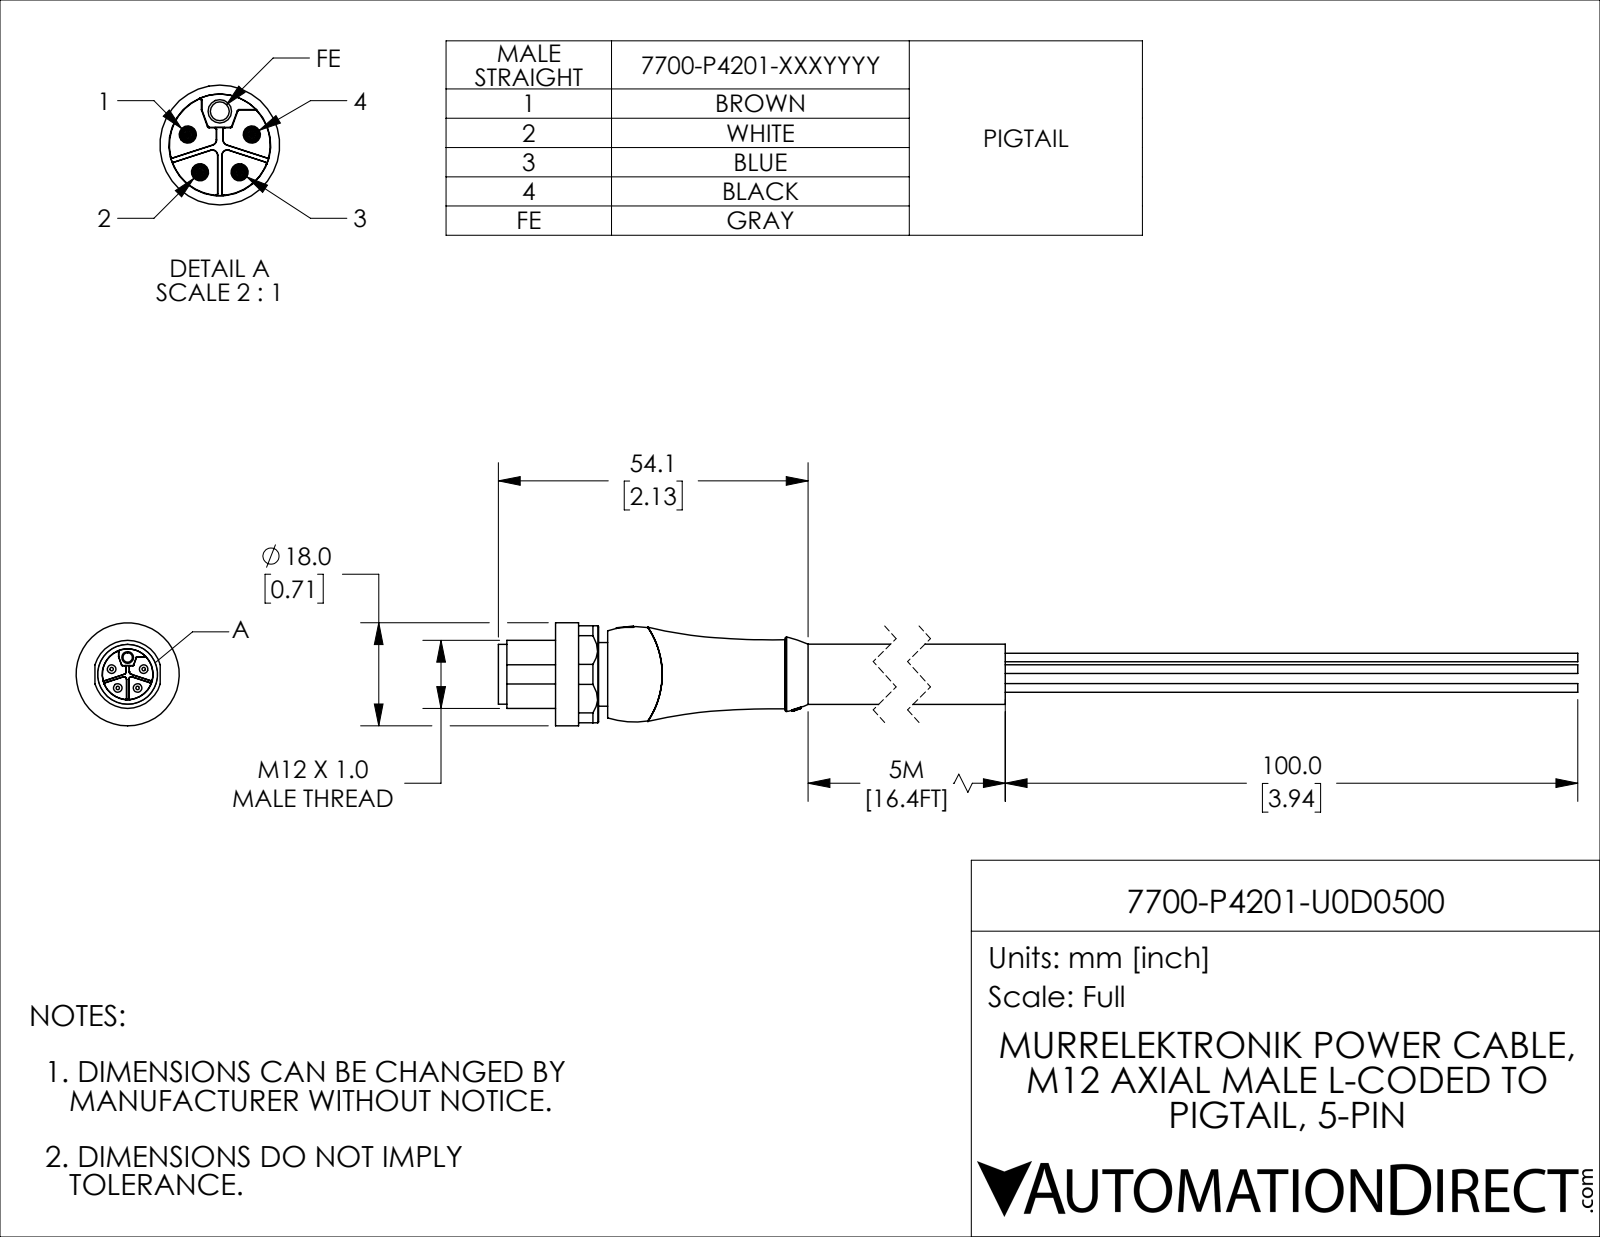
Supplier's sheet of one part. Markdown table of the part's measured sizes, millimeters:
| quantity | value |
| --- | --- |
| part name | 7700-P4201-U0D0500 |
| STEP written by | SolidWorks 2021 (CONFIG_CONTROL_DESIGN) |
| units | millimeters |
| bodies | 1 solid, 190 faces (87 planar, 51 cylindrical, 52 other) |
| overall size | 254.1 × 18 × 18 |
| volume | 17 489 mm³ |
| surface area | 9 110 mm² |
| round holes (diameter × count) | 1.65 × 1 |
| round bosses / shafts (diameter × count) | 1.5 × 5, 18 × 1, 11.88 × 1, 11.1 × 1, 10.5 × 1, 10.45 × 1 |
| partial cylindrical surfaces (radius × count) | 0.15 × 6, 1.13 × 1, 8.95 × 1 |
| main face-to-face distances | 9.1, 1.9, 7.2, 144.1, 136.9, 135, 16.94, 1.2, 8.4, 10.3 |
